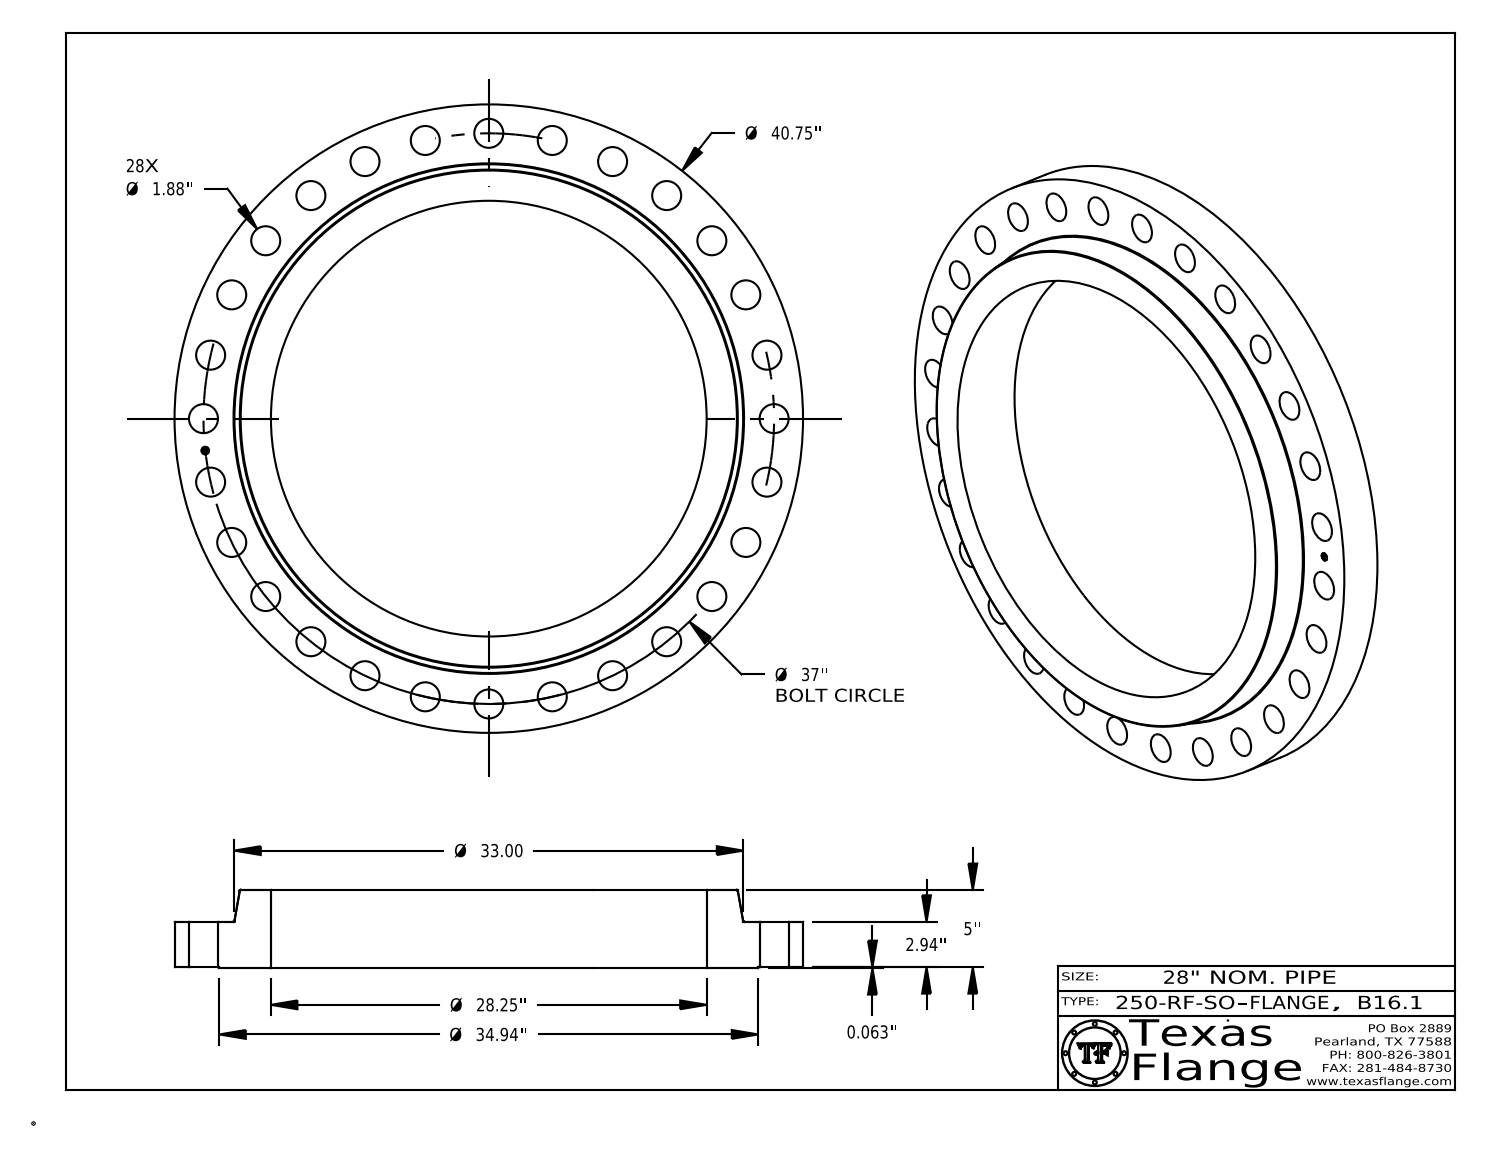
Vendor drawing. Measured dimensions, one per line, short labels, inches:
name: 250-RF-SO
written by: CATIA V5 STEP AP214 (AUTOMOTIVE_DESIGN)
unit: in
bodies: 1 solid, 457 faces (369 planar, 82 cylindrical, 6 other)
size: 40.75 × 40.75 × 5.063
volume: 2 216 in³; area: 2 692 in²
holes: 28× ⌀1.88, 1× ⌀0.495, 1× ⌀28.25
bosses: 8× ⌀0.03, 1× ⌀40.75, 1× ⌀34.94, 1× ⌀0.39
face distances: 3.003, 0.063, 2.94, 5.063, 5, 2.06, 2.988, 2.925, 0.015, 2.075
hole spacings: 18.5, 26.163, 31.329, 36.072, 36.767, 33.336, 4.143, 16.054
